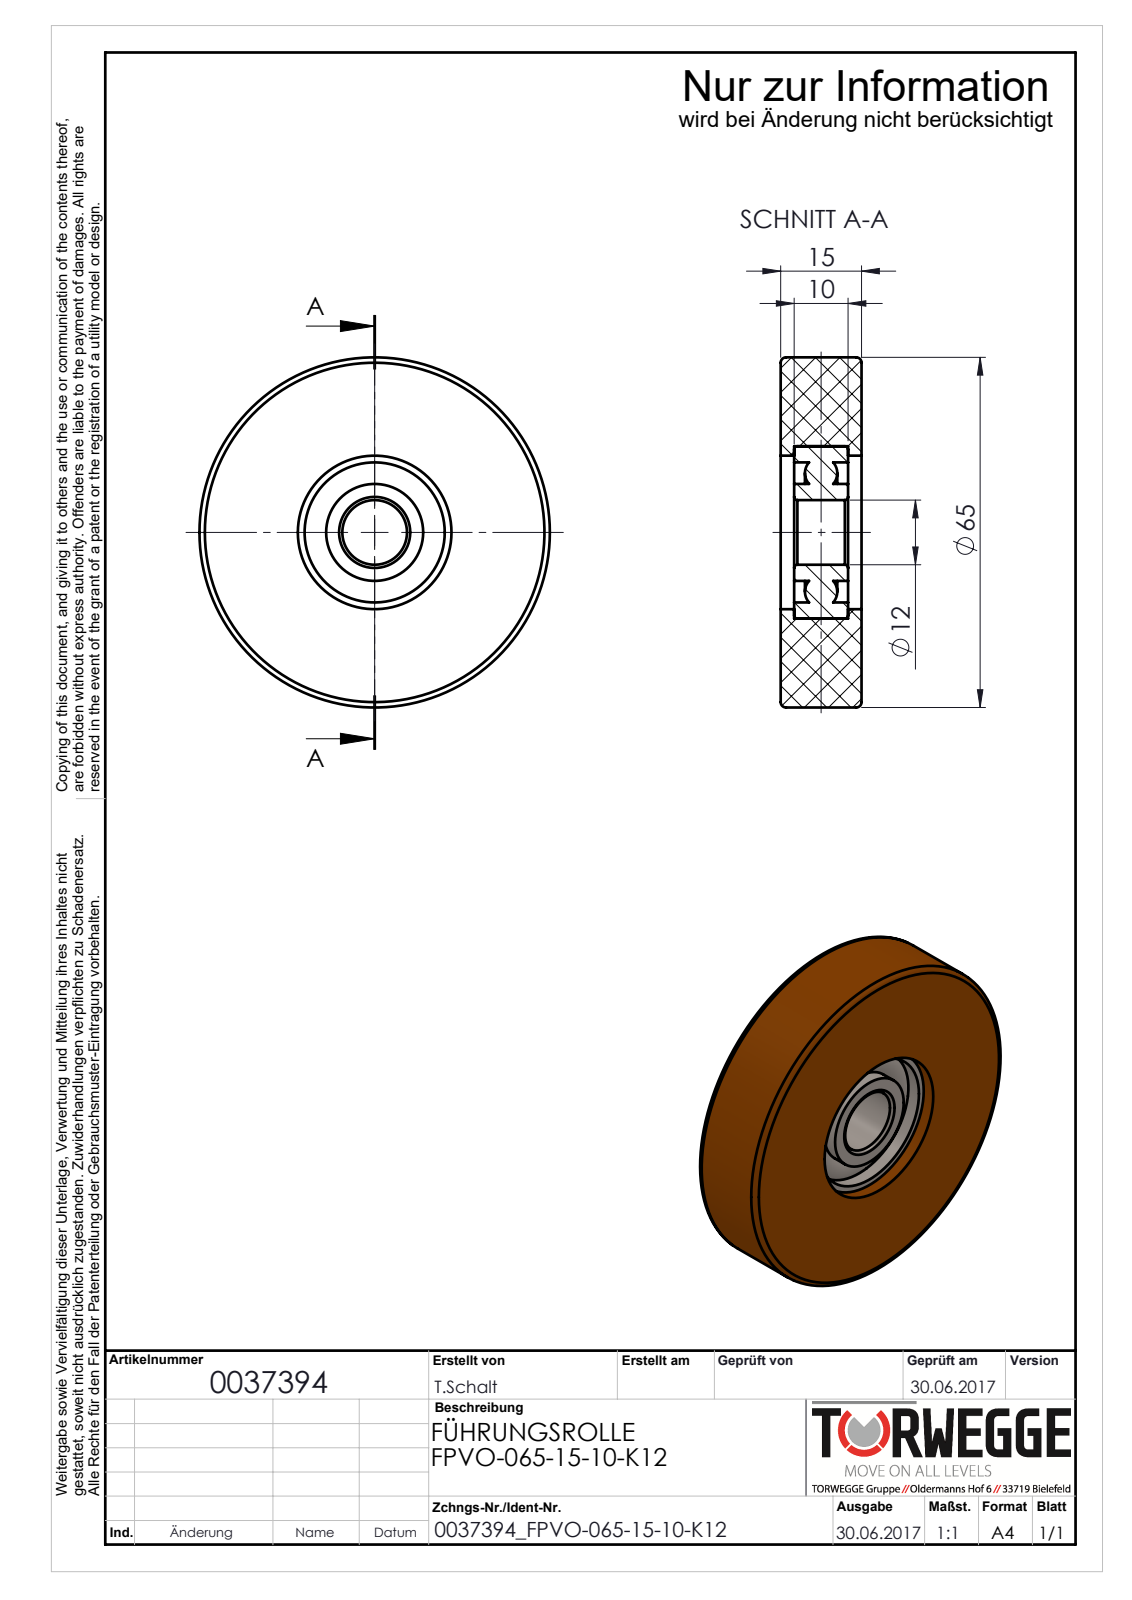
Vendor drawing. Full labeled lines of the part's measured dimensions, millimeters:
Part name (STEP PRODUCT): 0037394_FPVO-065-15-10-K12; FPVO-065-15-10-K12_Bandage; radial ball bearing_68_din_DIN 625 - 6201 - 8,SI,NC,8_68
STEP written by: SolidWorks 2016 (AUTOMOTIVE_DESIGN)
Units: millimetres
Bodies: 2 solids, 44 faces (8 planar, 20 cylindrical, 16 other)
Overall size (bounding box): 65 × 65 × 15
Volume: 44 107 mm³ · Surface area: 13 543 mm²
Round holes (diameter × count): ⌀12 ×1, ⌀26 ×1, ⌀28.5 ×1, ⌀32 ×1
Round bosses / shafts (diameter × count): ⌀65 ×1, ⌀18 ×1
Main face-to-face distances: 15, 2.5, 12.5, 10
